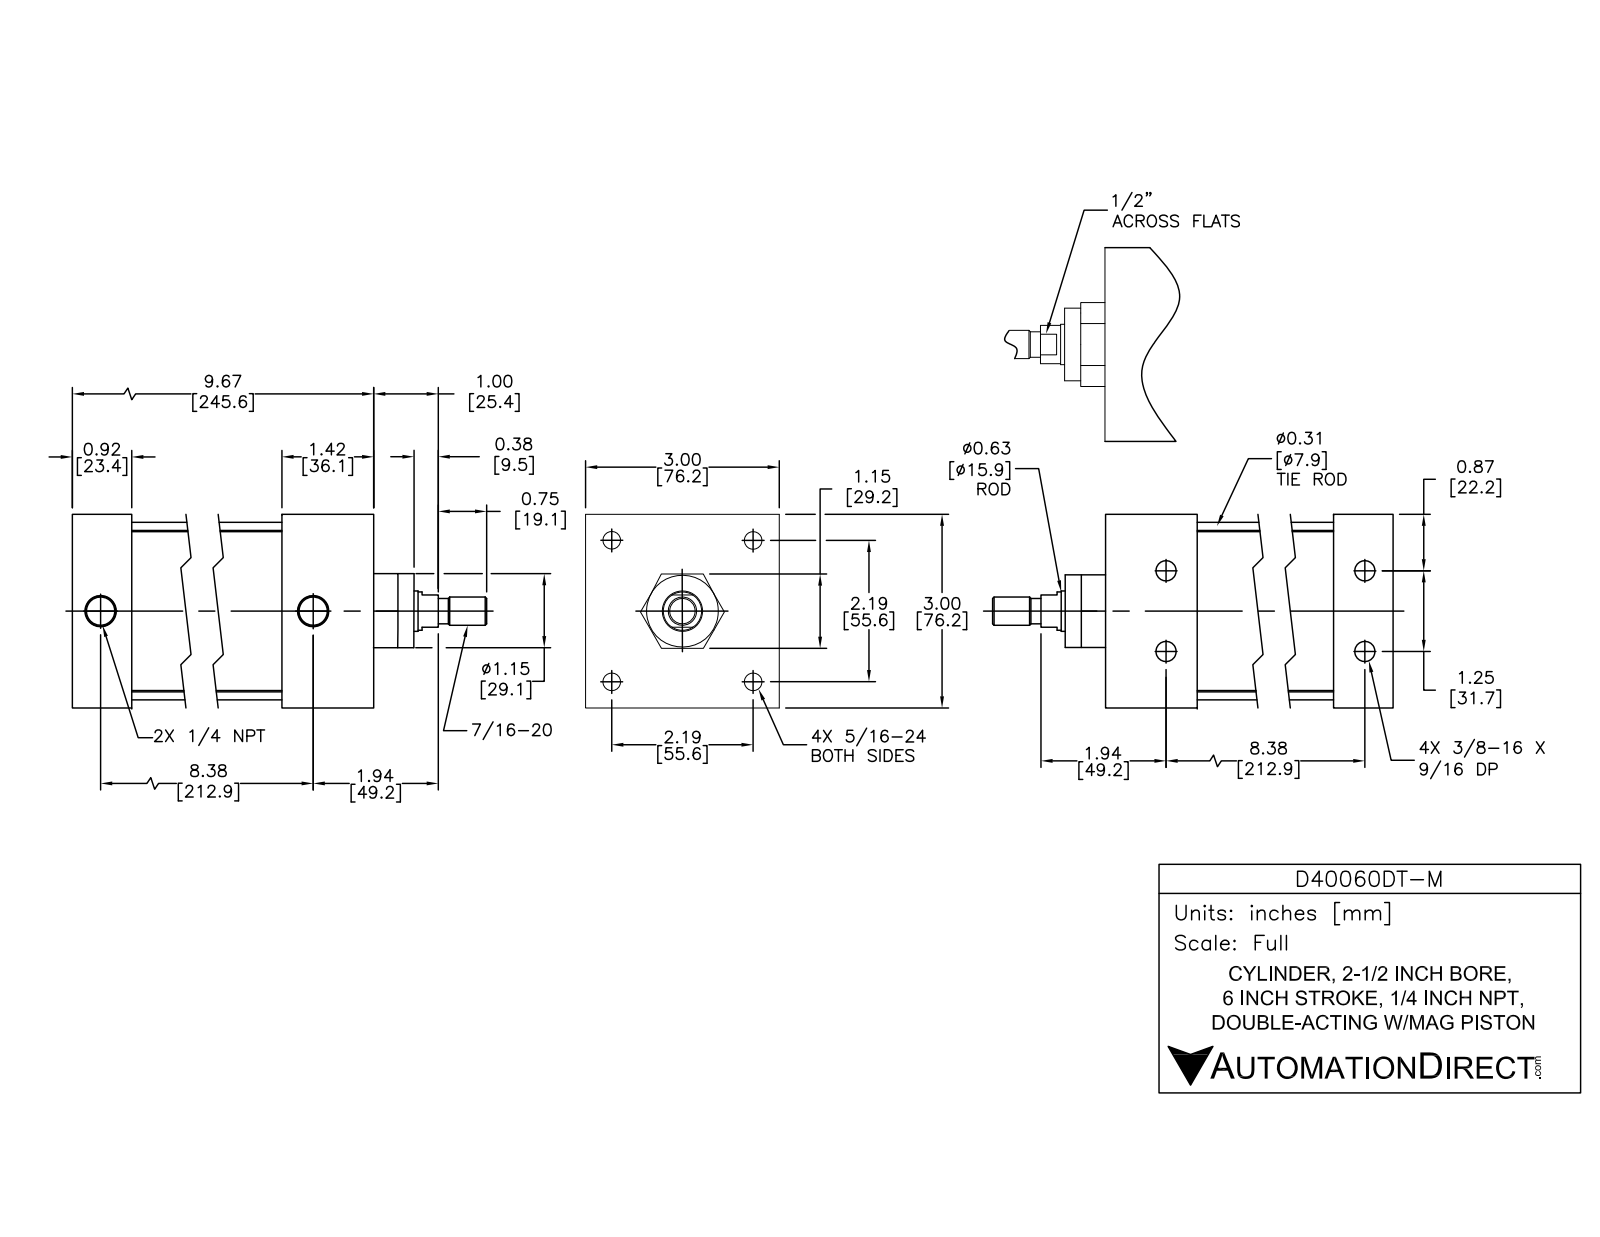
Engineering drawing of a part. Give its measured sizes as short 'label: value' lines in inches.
name: D40060DT-M PISTON; D40060DT-M BODY; D40060DT-M
written by: SolidWorks 2015 (AUTOMOTIVE_DESIGN)
unit: in
bodies: 12 solids, 298 faces (94 planar, 114 cylindrical, 90 other)
size: 11.496 × 3 × 3
volume: 38.72 in³; area: 284.6 in²
holes: 4× ⌀0.267, 4× ⌀0.307, 4× ⌀0.359, 4× ⌀0.5, 2× ⌀0.297, 2× ⌀0.477, 1× ⌀0.625, 1× ⌀0.628, 1× ⌀2.5
bosses: 4× ⌀0.484, 4× ⌀0.313, 4× ⌀0.282, 1× ⌀2.75, 1× ⌀2.497, 1× ⌀1.12, 1× ⌀0.622, 1× ⌀0.59
rounds: 4× R0.3
face distances: 3, 0.08, 7.326, 9.746, 8.726, 1.02, 1.42, 7.306, 8.326, 1
hole spacings: 1.556, 2.2, 8.393, 8.37, 0.625, 0.625, 1.25, 3.111
